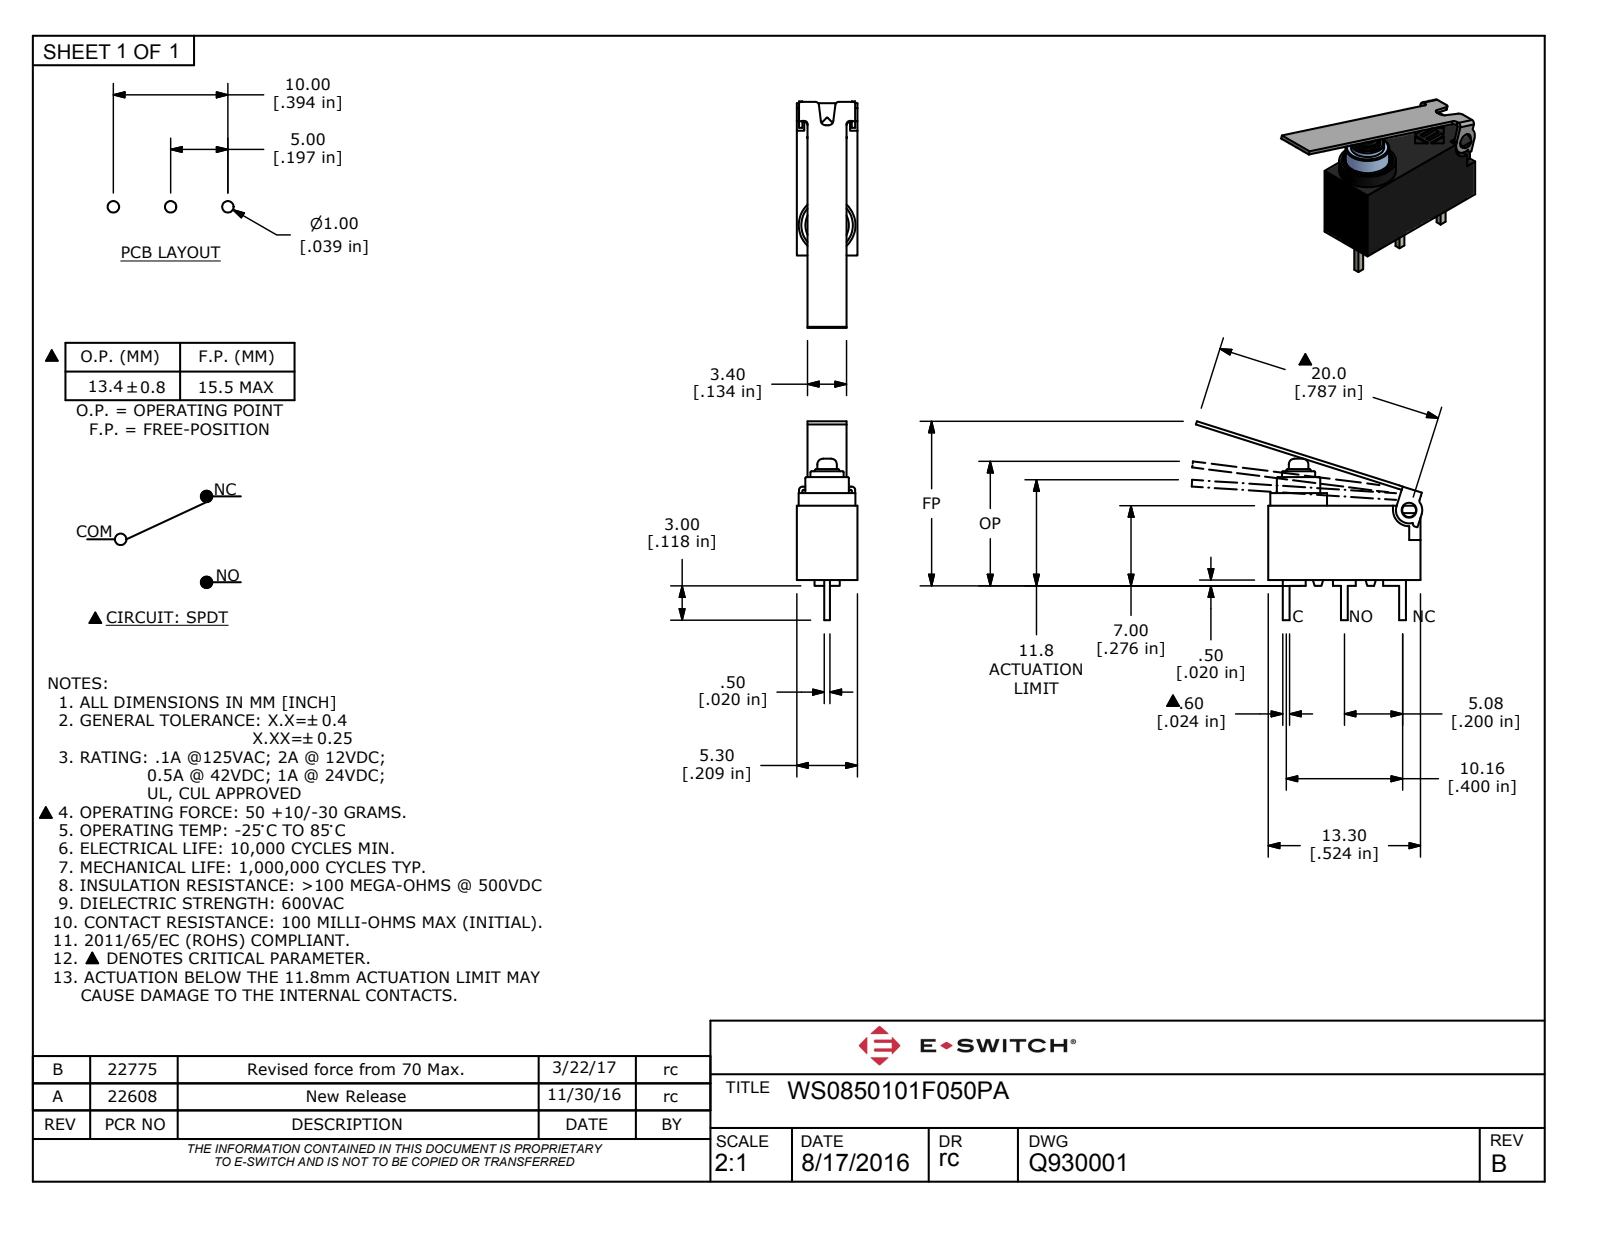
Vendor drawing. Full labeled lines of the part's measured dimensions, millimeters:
Part name (STEP PRODUCT): P:\\E-Switch Secure\\3D_MODELS_STP_FORMAT\\WS0850101F050PA.stp
STEP written by: ACIS (CONFIG_CONTROL_DESIGN)
Units: millimetres
Bodies: 2 solids, 169 faces (113 planar, 49 cylindrical, 7 other)
Overall size (bounding box): 19.8 × 17.4 × 5.3
Volume: 520 mm³ · Surface area: 650 mm²
Round holes (diameter × count): ⌀1.3 ×1, ⌀4.5 ×1
Round bosses / shafts (diameter × count): ⌀5 ×1, ⌀3.8 ×1, ⌀2.9 ×1, ⌀1.7 ×1
Partial cylindrical surfaces — rounded edges, fillets, slot ends (radius × count): R0.3 ×6, R0.1 ×2, R0.3 ×2, R0.5 ×2, R0.6 ×1, R1.1 ×1, R1.4 ×1
Main face-to-face distances: 5.3, 6.5, 13.3, 2.4, 0.5, 2.9, 0.5, 4.1, 0.6, 6.4
